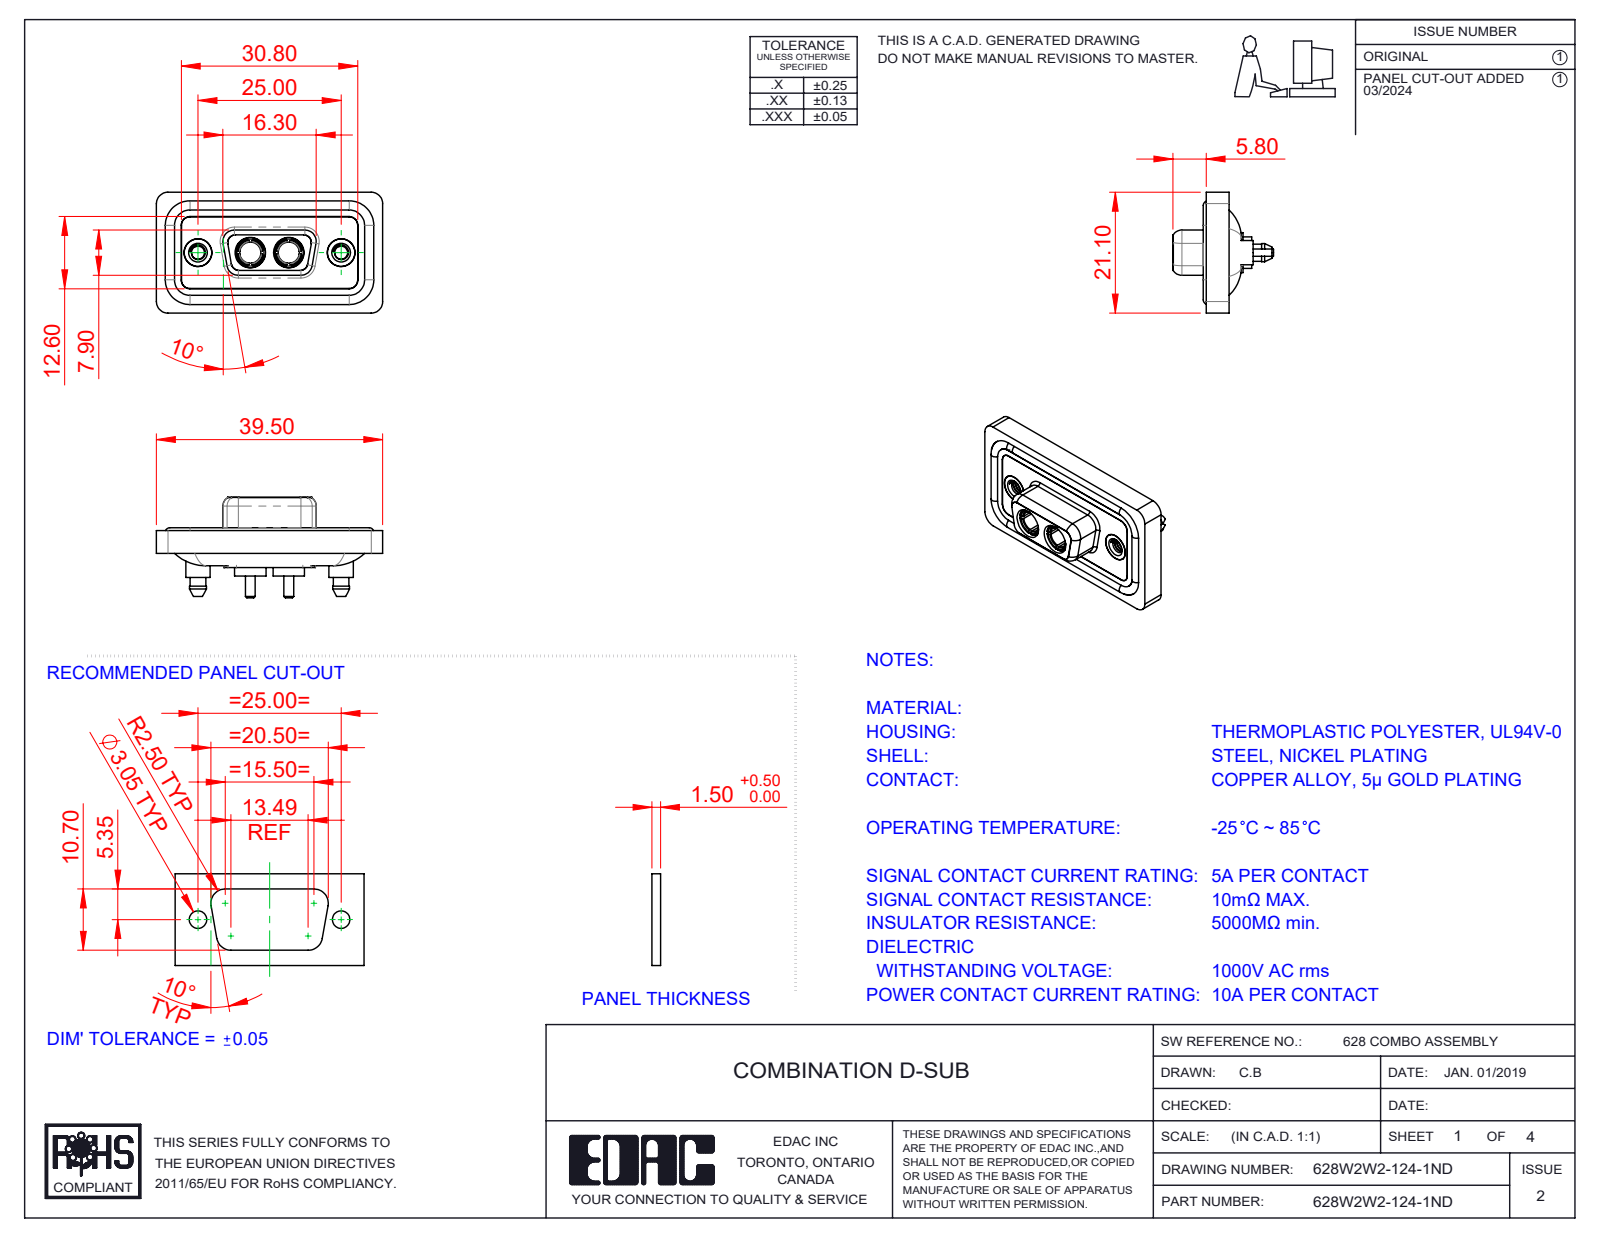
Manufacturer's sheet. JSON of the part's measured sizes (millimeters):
{"part_name": "628Combo Shell Front_09 Contacts; 628W2W2-124-1ND; 628Combo Threaded Boardlock_D; 628Combo Waterproof Housing_09 Contacts (+3 more)", "step_written_by": "SolidWorks 2023 (CONFIG_CONTROL_DESIGN)", "units": "millimeters", "bodies": {"solids": 11, "faces": 600, "planar": 179, "cylindrical": 282, "other": 139}, "overall_size": [39.5, 21.1, 17.55], "volume_mm3": 4819, "surface_area_mm2": 7950, "round_holes": [[4.85, 4], [2.26, 2], [3.7, 2], [4, 2], [4.05, 2], [5, 2], [5.3, 2]], "round_bosses_or_shafts": [[1.6, 4], [5.5, 2], [5.4, 2], [5.2, 2], [4.96, 2], [4.95, 2], [4.8, 2], [4.75, 2]], "partial_cylinders_radius": [[1.5, 24], [2, 18], [1.6, 10], [1.35, 8], [0.25, 4], [0.5, 4], [0.6, 4], [0.65, 4]], "face_to_face_distances": [0.4, 1.8, 1.1, 2.9, 1.6, 0.5, 5.65, 1.5, 7.45, 4], "hole_center_spacings": [9.14, 15.86, 6.72, 25]}
